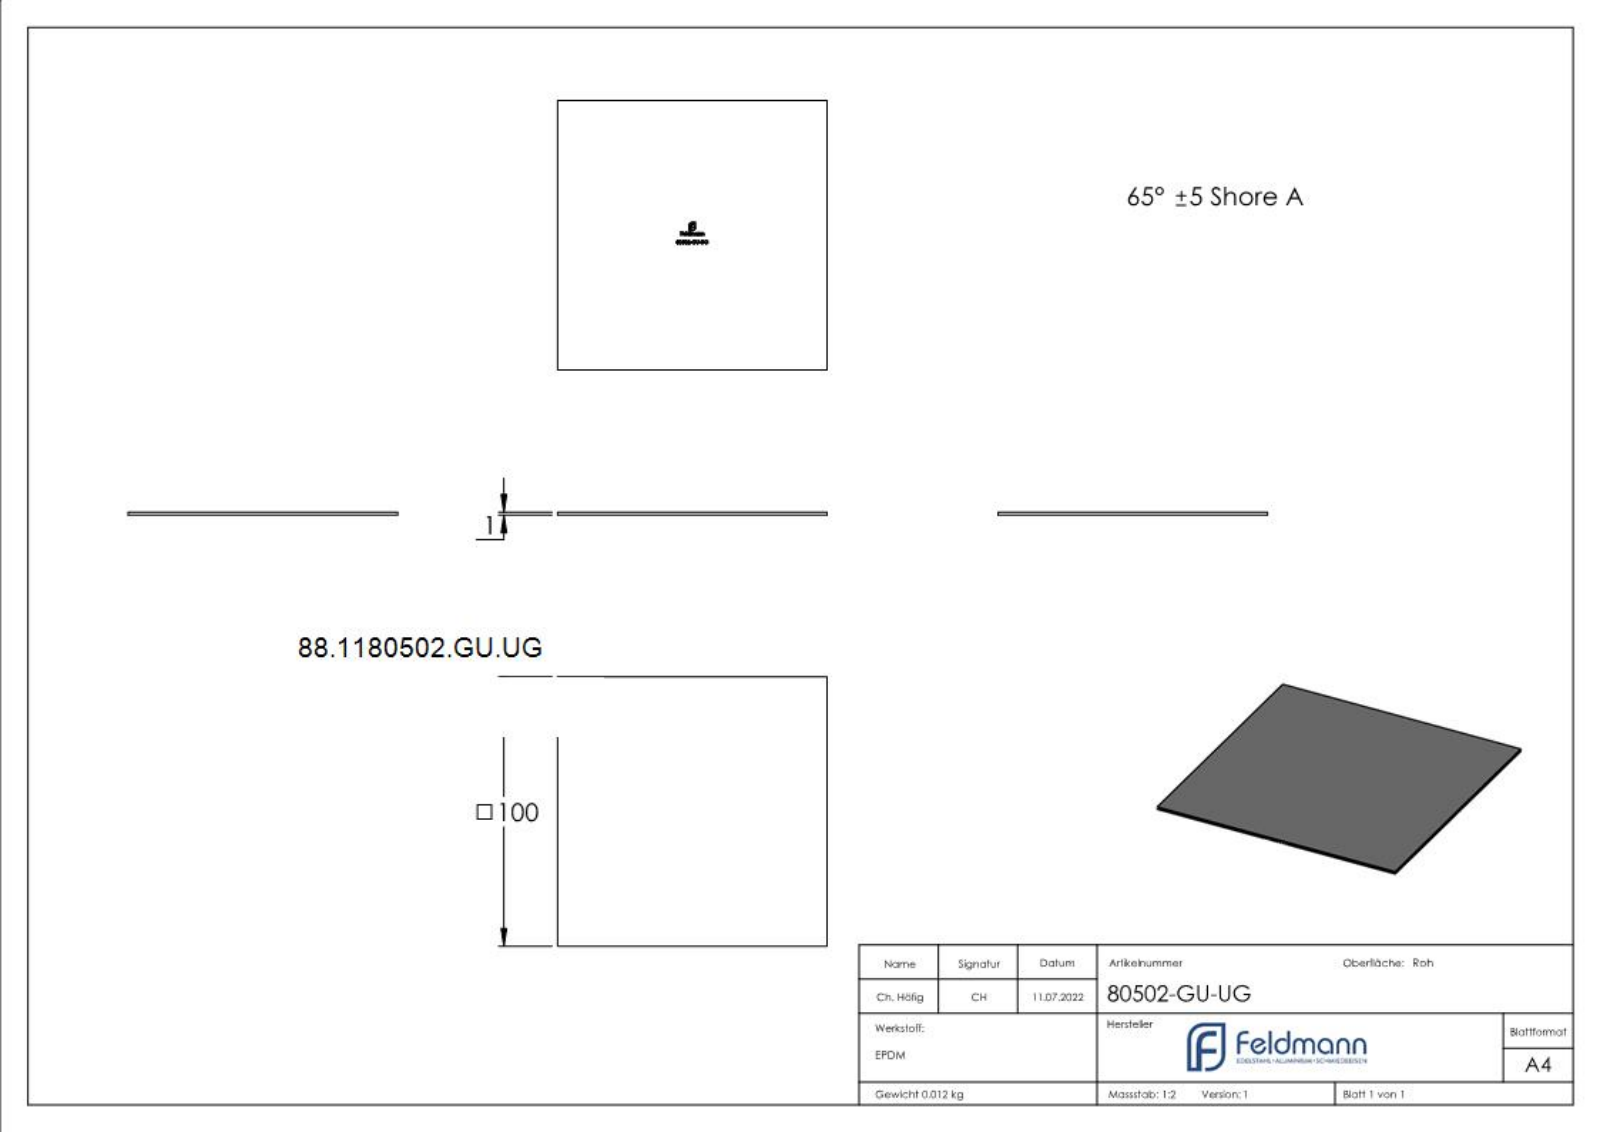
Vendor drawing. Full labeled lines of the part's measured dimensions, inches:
Part name (STEP PRODUCT): 80502-GU-UG
STEP written by: SolidWorks 2018 (CONFIG_CONTROL_DESIGN)
Units: inches
Bodies: 1 solid, 298 faces (149 planar, 0 cylindrical, 149 other)
Overall size (bounding box): 3.937 × 3.937 × 0.039
Volume: 0.61 in³ · Surface area: 31.64 in²
Main face-to-face distances: 0.039, 3.937, 0.035, 0.023, 0.072, 0.117, 0.106, 0.013, 0.087, 1.969
